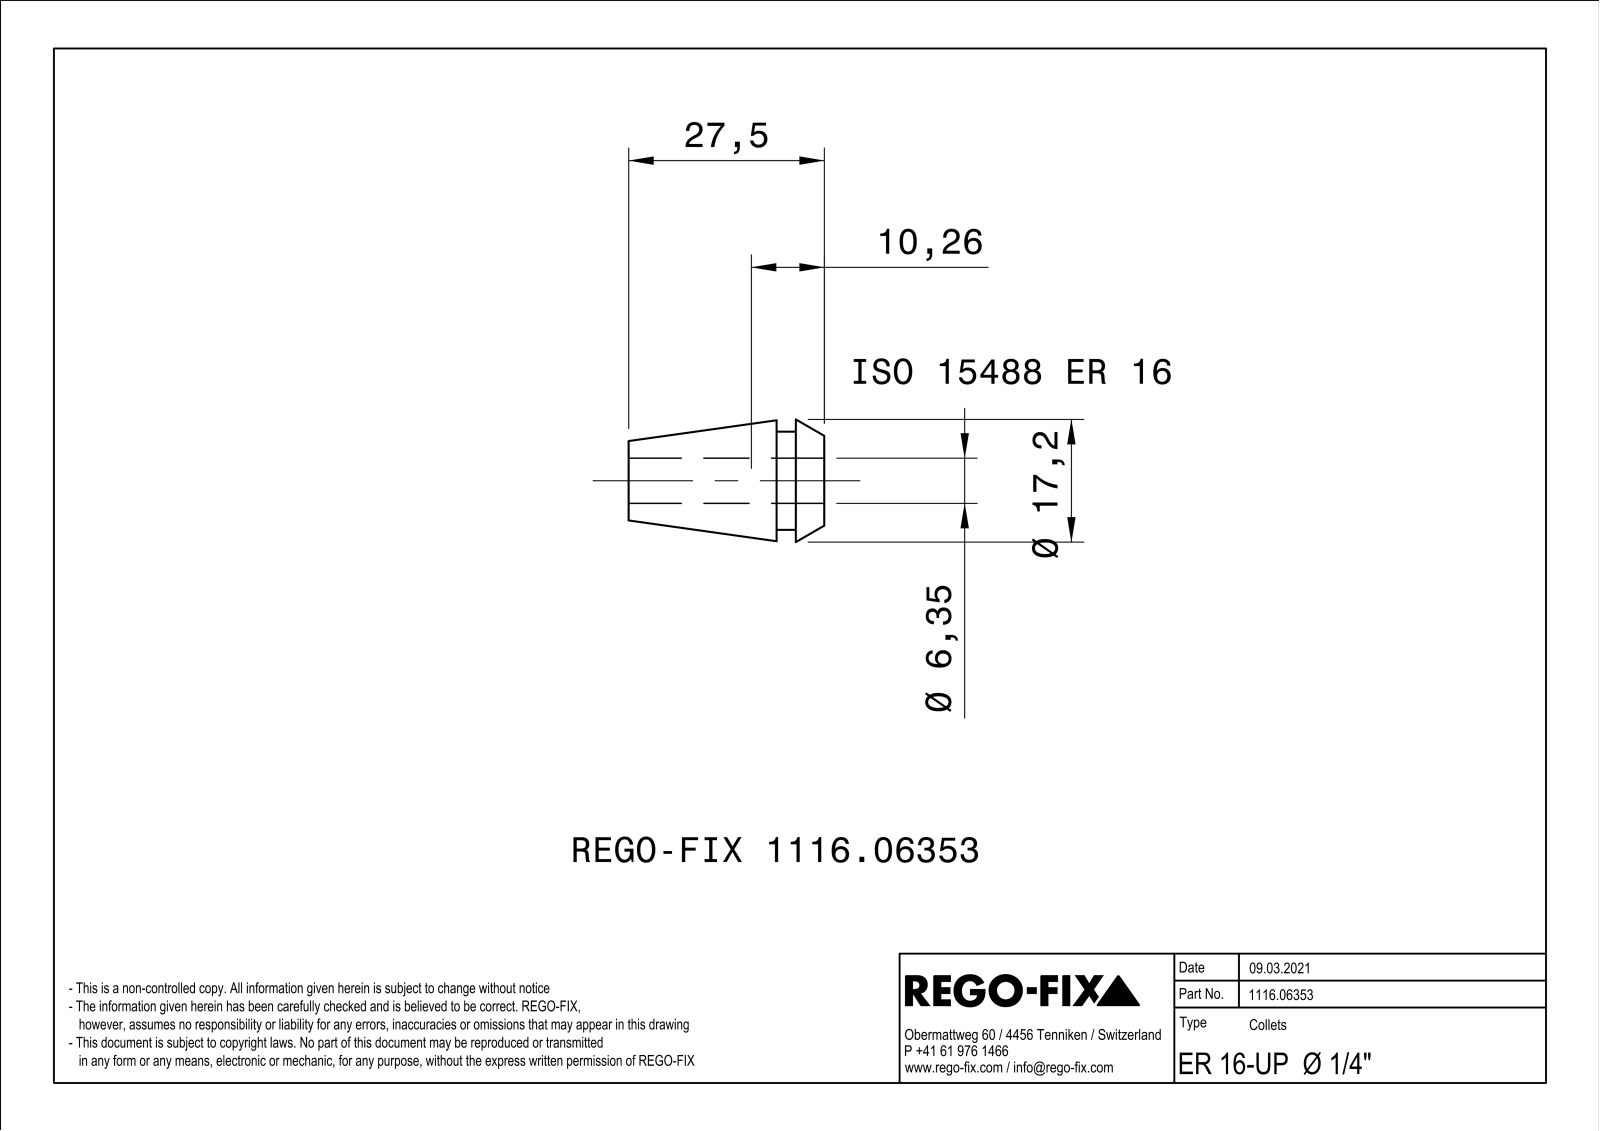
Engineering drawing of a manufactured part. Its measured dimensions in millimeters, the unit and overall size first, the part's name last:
Units: millimetres
Overall size (bounding box): 27.5 × 17.24 × 17.24
Round holes (diameter × count): ⌀6.35 ×1
Round bosses / shafts (diameter × count): ⌀13.8 ×1
Partial cylindrical surfaces — rounded edges, fillets, slot ends (radius × count): R0.3 ×8
Main face-to-face distances: 0.6, 4, 6.7, 2.7, 27.5, 23.5, 20.8
Volume: 2 609 mm³ · Surface area: 4 676 mm²
Bodies: 1 solid, 153 faces (72 planar, 25 cylindrical, 56 other)
Part name (STEP PRODUCT): NOCUT
STEP written by: SIEMENS PLM Software Solid Edge ST10 (AUTOMOTIVE_DESIGN)
